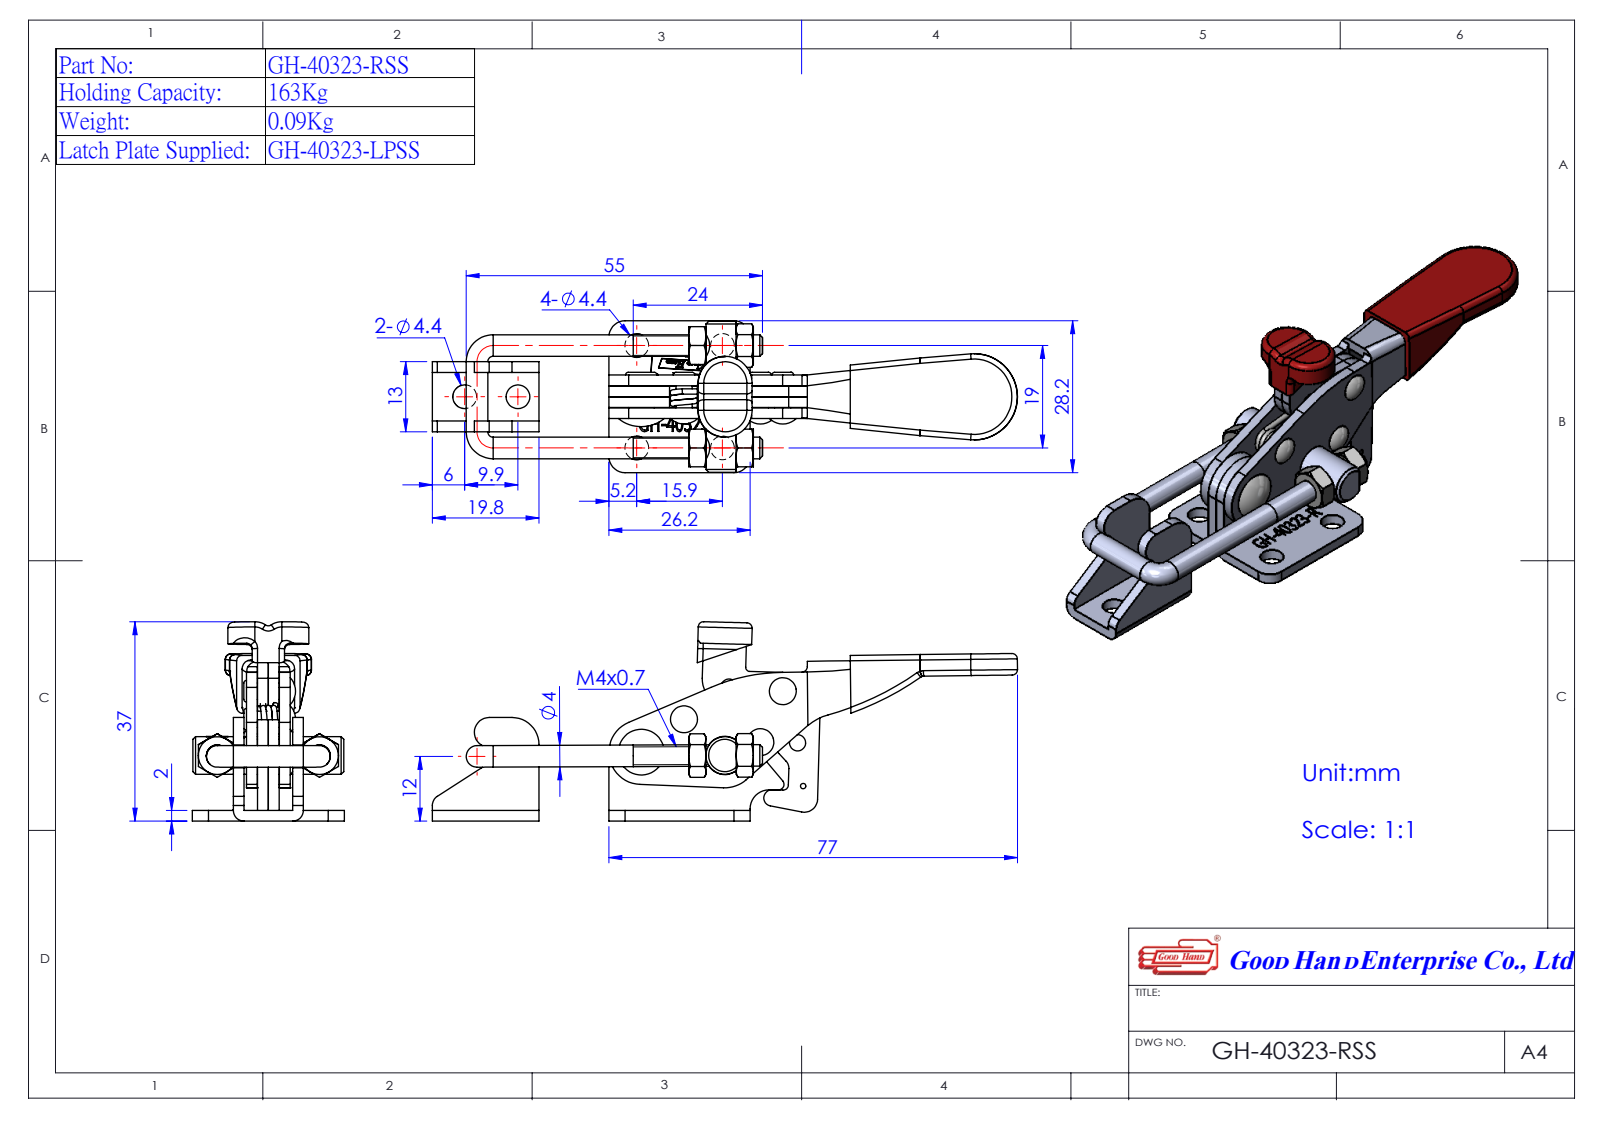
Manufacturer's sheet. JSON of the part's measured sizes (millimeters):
{"part_name": "GH-40323-RSS(簡化); 140323LP-1^GH-40323-RSS(簡化); Group4^GH-40323-RSS(簡化); Group3^GH-40323-RSS(簡化) (+2 more)", "step_written_by": "SolidWorks 2016 (AUTOMOTIVE_DESIGN)", "units": "millimeters", "bodies": {"solids": 7, "faces": 659, "planar": 291, "cylindrical": 151, "other": 217}, "overall_size": [108.63, 37.02, 28.2], "volume_mm3": 13552, "surface_area_mm2": 13083, "round_holes": [[4.4, 6], [3.3, 2], [4, 2], [4.2, 2], [1.34, 1], [3.8, 1]], "round_bosses_or_shafts": [[4, 3], [6.8, 2], [3, 2], [7, 1], [1.28, 1]], "partial_cylinders_radius": [[1, 8], [2, 6], [3, 4], [3.5, 4], [5, 4], [0.51, 3], [0.54, 3], [6, 3]], "face_to_face_distances": [2, 4.05, 2.05, 2.45, 8.55, 6.05, 6.1, 4, 8.5, 4.1], "hole_center_spacings": [19, 15.9, 24, 24.78, 33.32, 39.11, 48.77, 7.13]}
